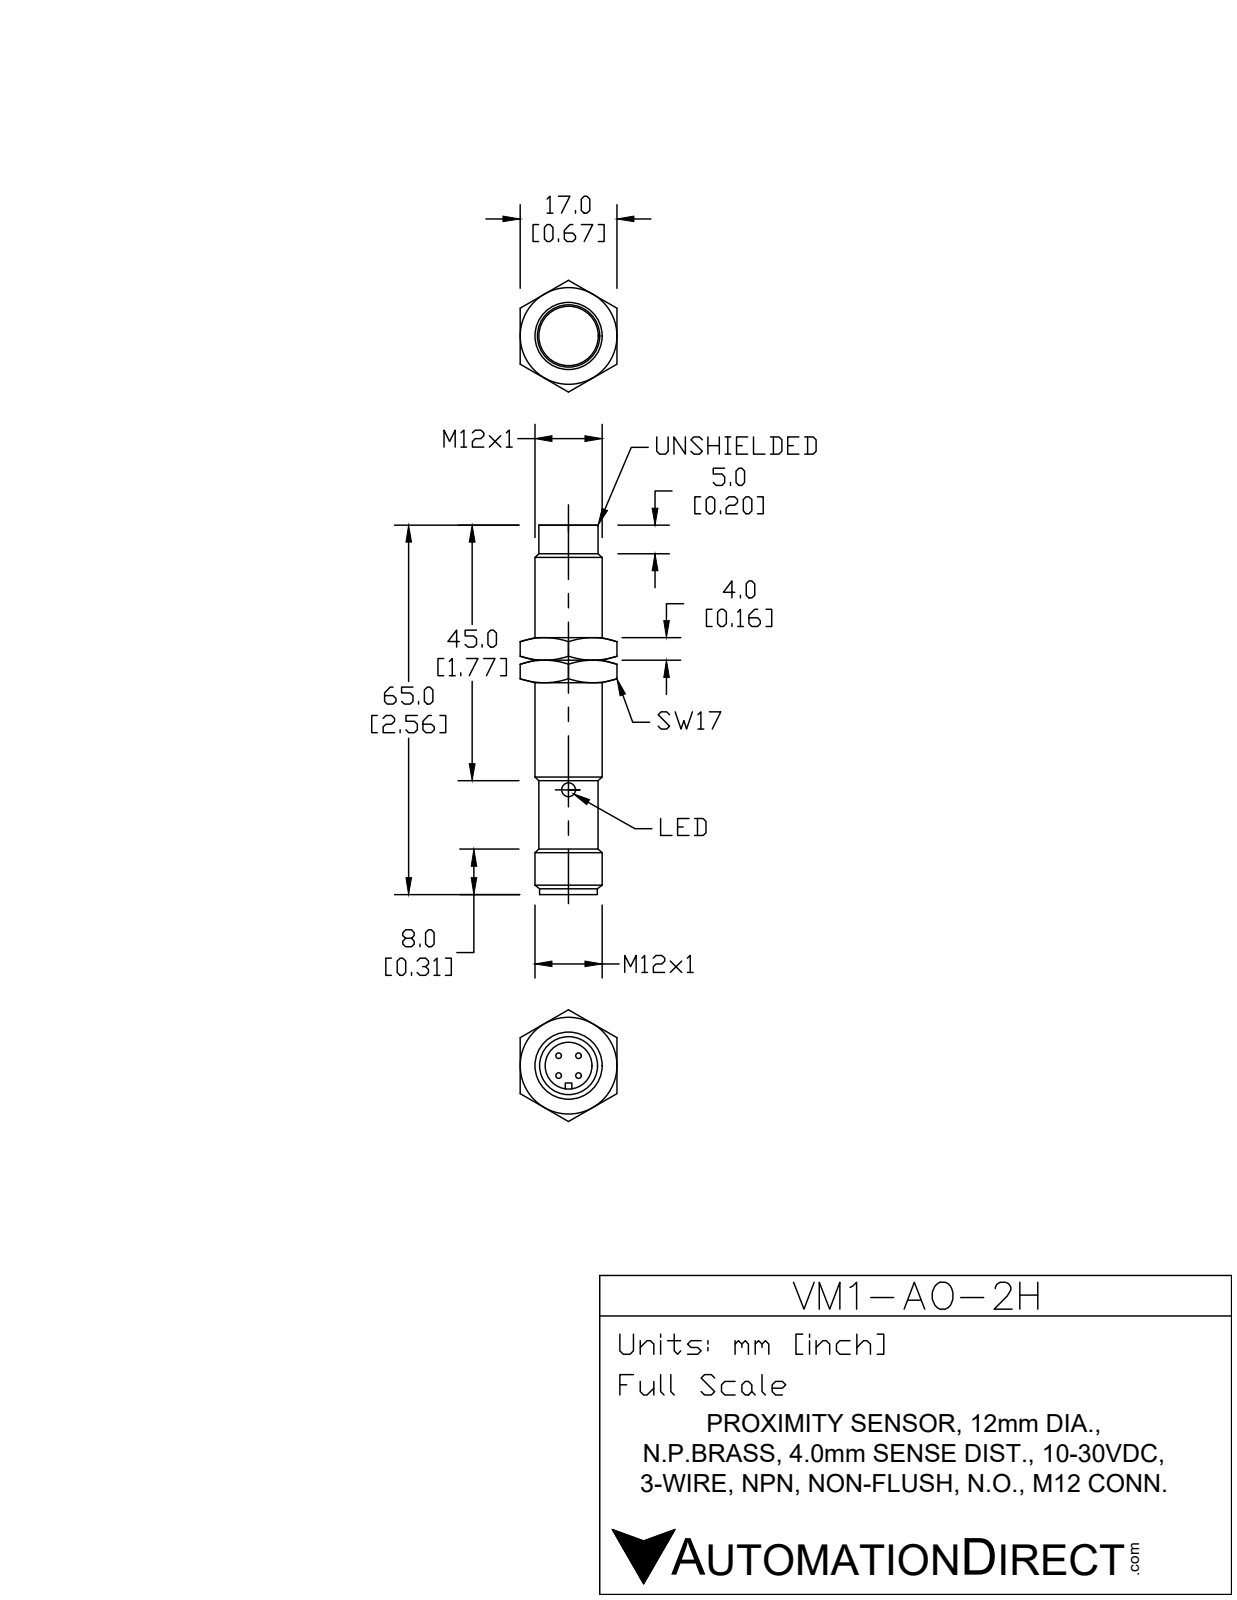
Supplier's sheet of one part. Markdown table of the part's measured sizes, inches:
| quantity | value |
| --- | --- |
| part name | VM1-A0-2H |
| STEP written by | SolidWorks 2017 (AUTOMOTIVE_DESIGN) |
| units | inches |
| bodies | 3 solids, 99 faces (22 planar, 49 cylindrical, 28 other) |
| overall size | 2.559 × 0.472 × 0.472 |
| volume | 0.385 in³ |
| surface area | 6.079 in² |
| round holes (diameter × count) | 0.098 × 1, 0.331 × 1, 0.374 × 1 |
| round bosses / shafts (diameter × count) | 0.039 × 4, 0.472 × 1, 0.413 × 1, 0.382 × 1, 0.378 × 1 |
| partial cylindrical surfaces (radius × count) | 0.051 × 4, 0.02 × 1, 0.024 × 1, 0.051 × 1, 0.134 × 1 |
| main face-to-face distances | 0.197, 2.122, 1.925, 2.147, 1.95, 0.025, 2.52, 2.323, 0.398, 0.373 |
